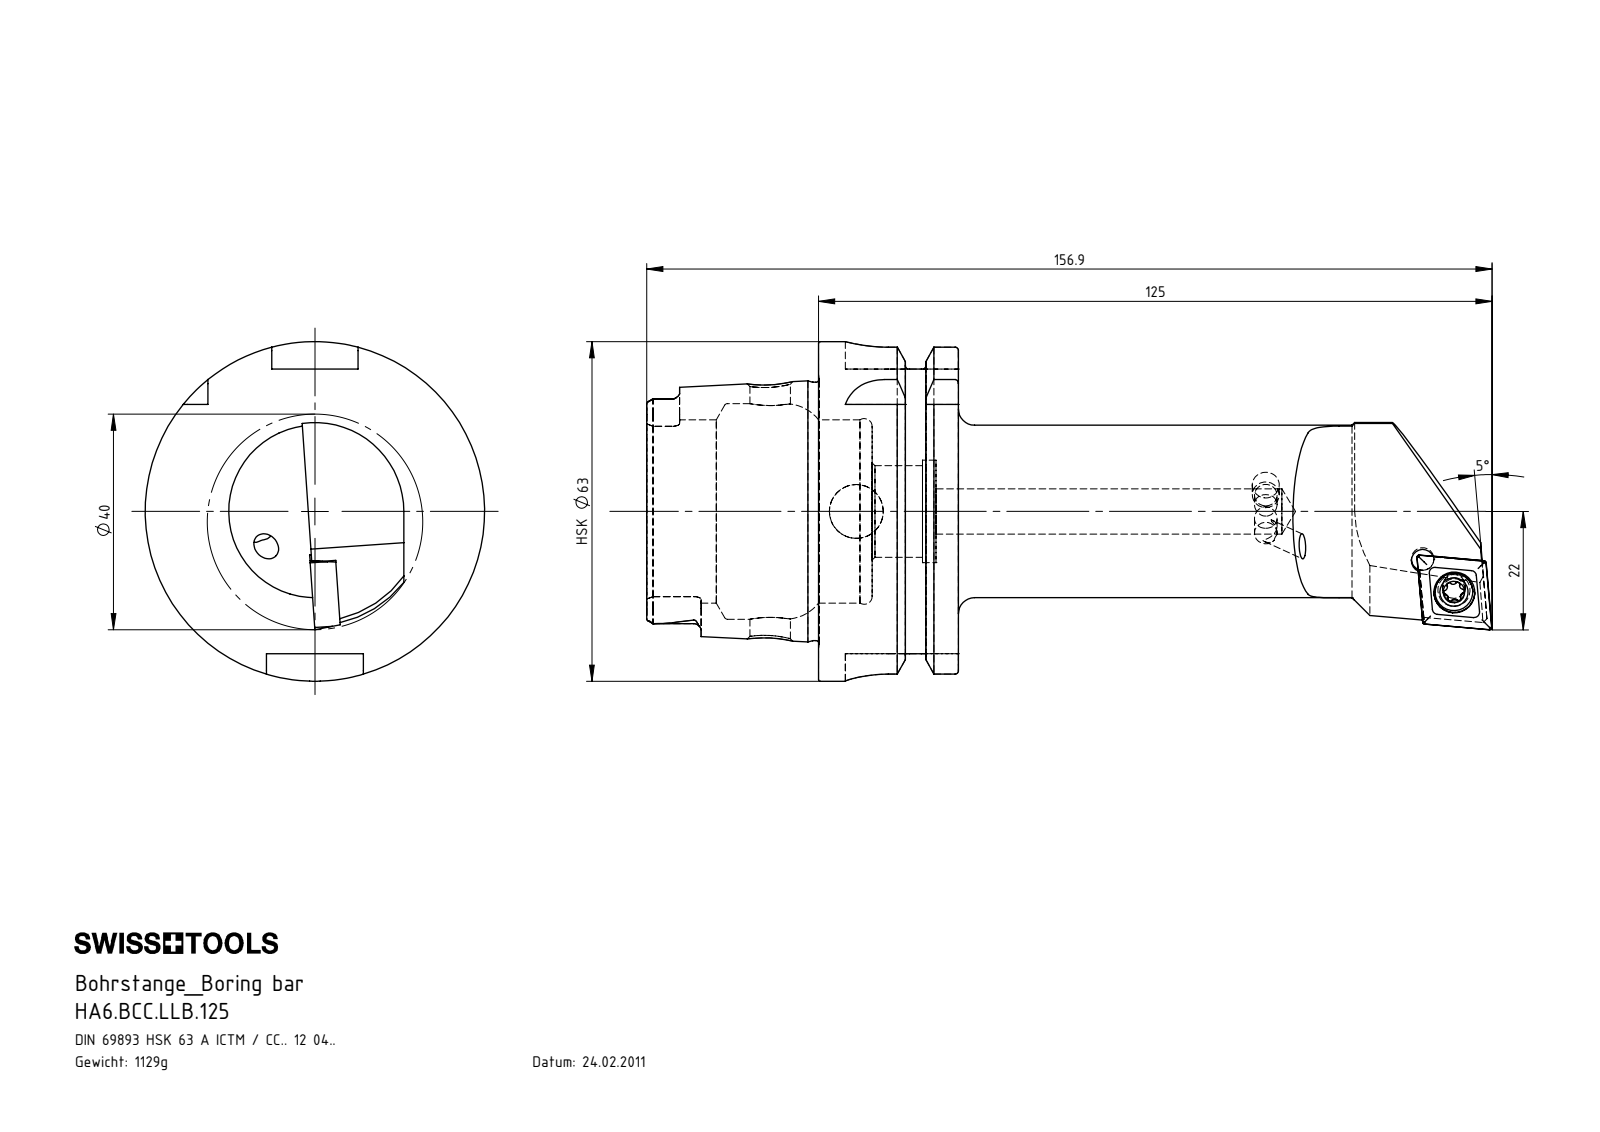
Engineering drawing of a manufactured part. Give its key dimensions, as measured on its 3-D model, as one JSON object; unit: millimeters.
{"part_name": "HA6-BCC.LLB.125_A; WCC-ER2.001.010_A; HA6.BCC.LLB.125; CCMT120404 (+1 more)", "step_written_by": "SolidWorks 2017 (AUTOMOTIVE_DESIGN)", "units": "millimeters", "bodies": {"solids": 5, "faces": 298, "planar": 71, "cylindrical": 91, "other": 136}, "overall_size": [156.86, 63, 63], "volume_mm3": 143985, "surface_area_mm2": 34325, "round_holes": [[4.2, 4], [4, 1], [5.5, 1], [7.5, 1], [7.6, 1], [8.4, 1], [10, 1], [17, 1], [19, 1], [34, 1], [40, 1]], "round_bosses_or_shafts": [[5, 2], [63, 1], [54.95, 1], [47.94, 1], [32, 1], [7, 1]], "partial_cylinders_radius": [[0.39, 6], [1.4, 6], [8, 4], [0.69, 3], [0.69, 3], [2.82, 2], [2.88, 2], [3, 1]], "face_to_face_distances": [25.95, 16, 9.95, 31.9, 41.85, 57.85, 52.8, 21.8, 11.85, 53.7], "hole_center_spacings": [8.21, 8.32]}
